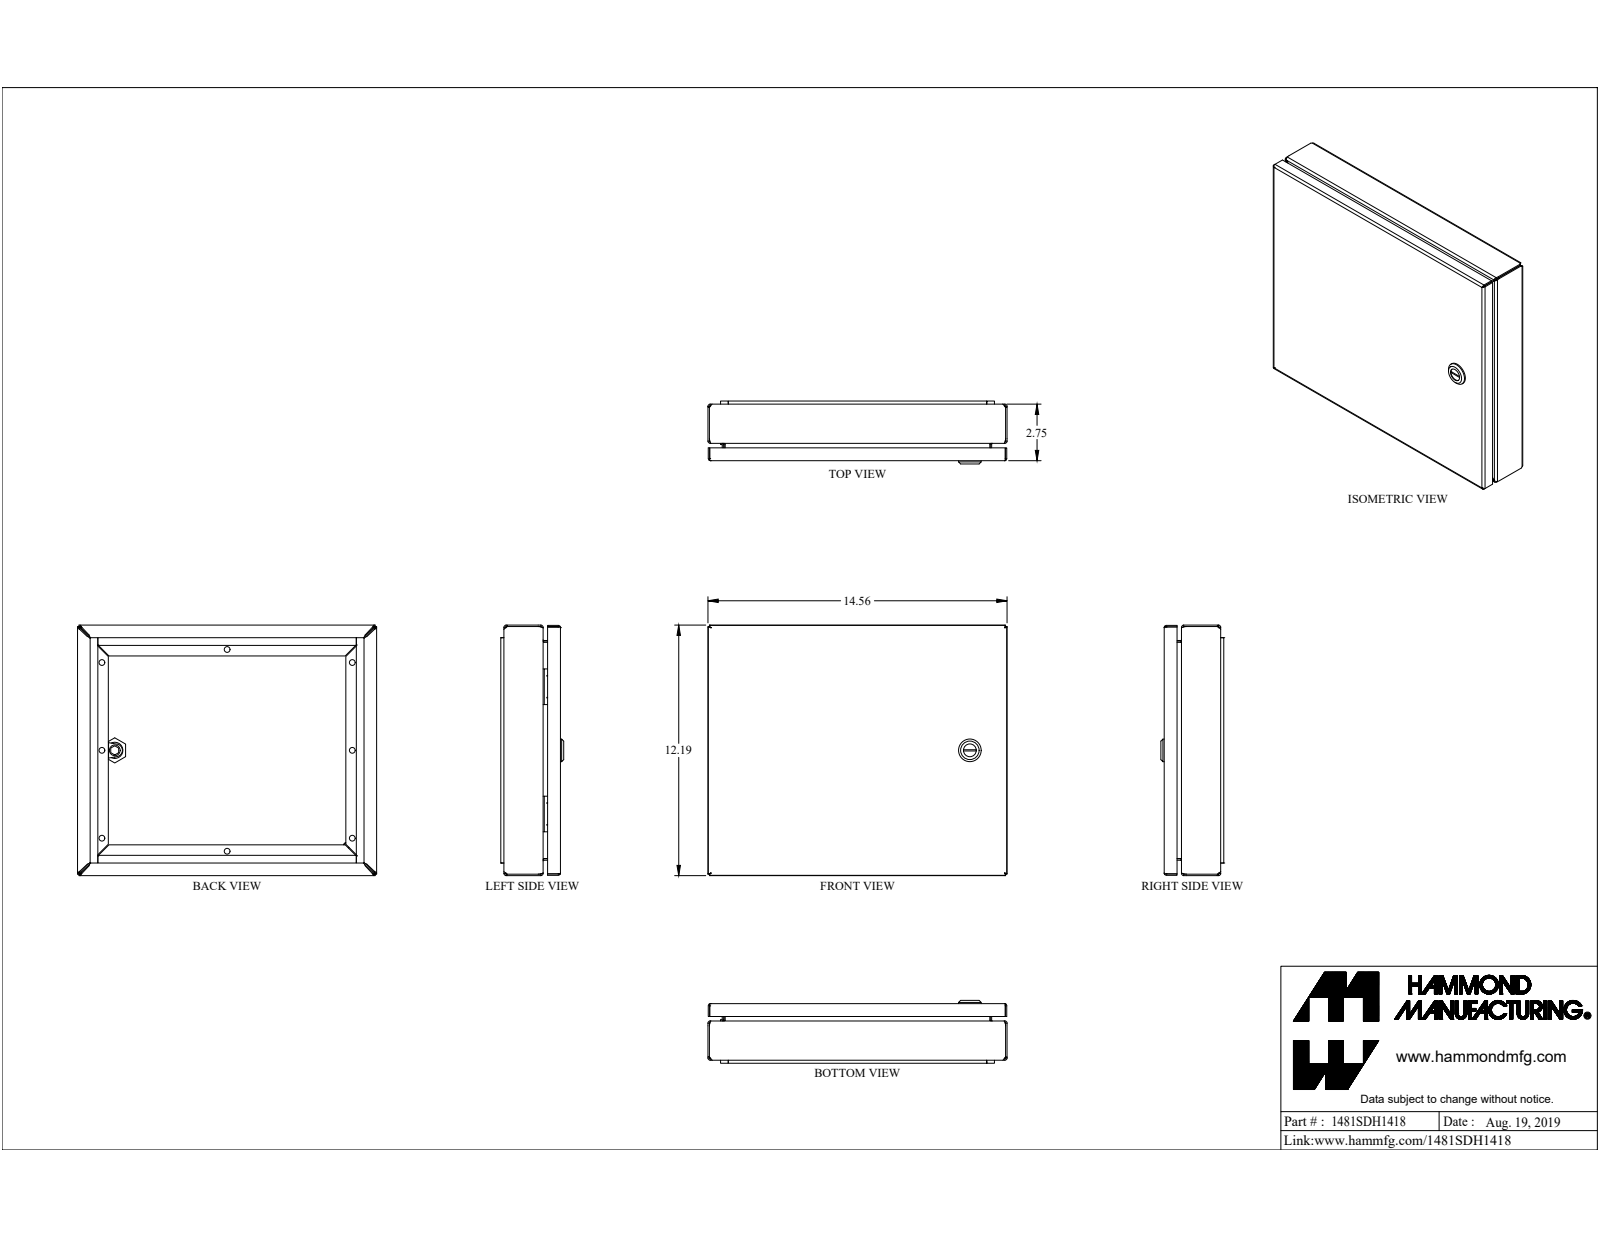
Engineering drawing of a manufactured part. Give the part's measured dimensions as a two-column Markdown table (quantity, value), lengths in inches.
| quantity | value |
| --- | --- |
| part name | 1481SDH1418 |
| STEP written by | SolidWorks 2019 (CONFIG_CONTROL_DESIGN) |
| units | inches |
| bodies | 23 solids, 614 faces (348 planar, 168 cylindrical, 98 other) |
| overall size | 14.56 × 12.19 × 3.061 |
| volume | 41.88 in³ |
| surface area | 1 087 in² |
| round holes (diameter × count) | 0.281 × 8, 0.172 × 1, 0.232 × 1, 0.24 × 1, 0.242 × 1, 0.625 × 1, 0.785 × 1 |
| round bosses / shafts (diameter × count) | 1.1 × 1, 0.525 × 1, 0.455 × 1, 0.398 × 1, 0.356 × 1, 0.313 × 1, 0.292 × 1, 0.25 × 1 |
| partial cylindrical surfaces (radius × count) | 0.036 × 28, 0.108 × 28, 0.382 × 12, 19.003 × 8, 0.006 × 4, 0.062 × 4, 0.25 × 4, 0.499 × 4 |
| main face-to-face distances | 0.072, 2.579, 0.843, 1.736, 2.651, 12.118, 14.488, 2.507, 2.679, 1.836 |
| hole center spacings | 6.125, 7.822, 11.017, 12.912, 12.184, 4.273, 4.273, 8.546 |
